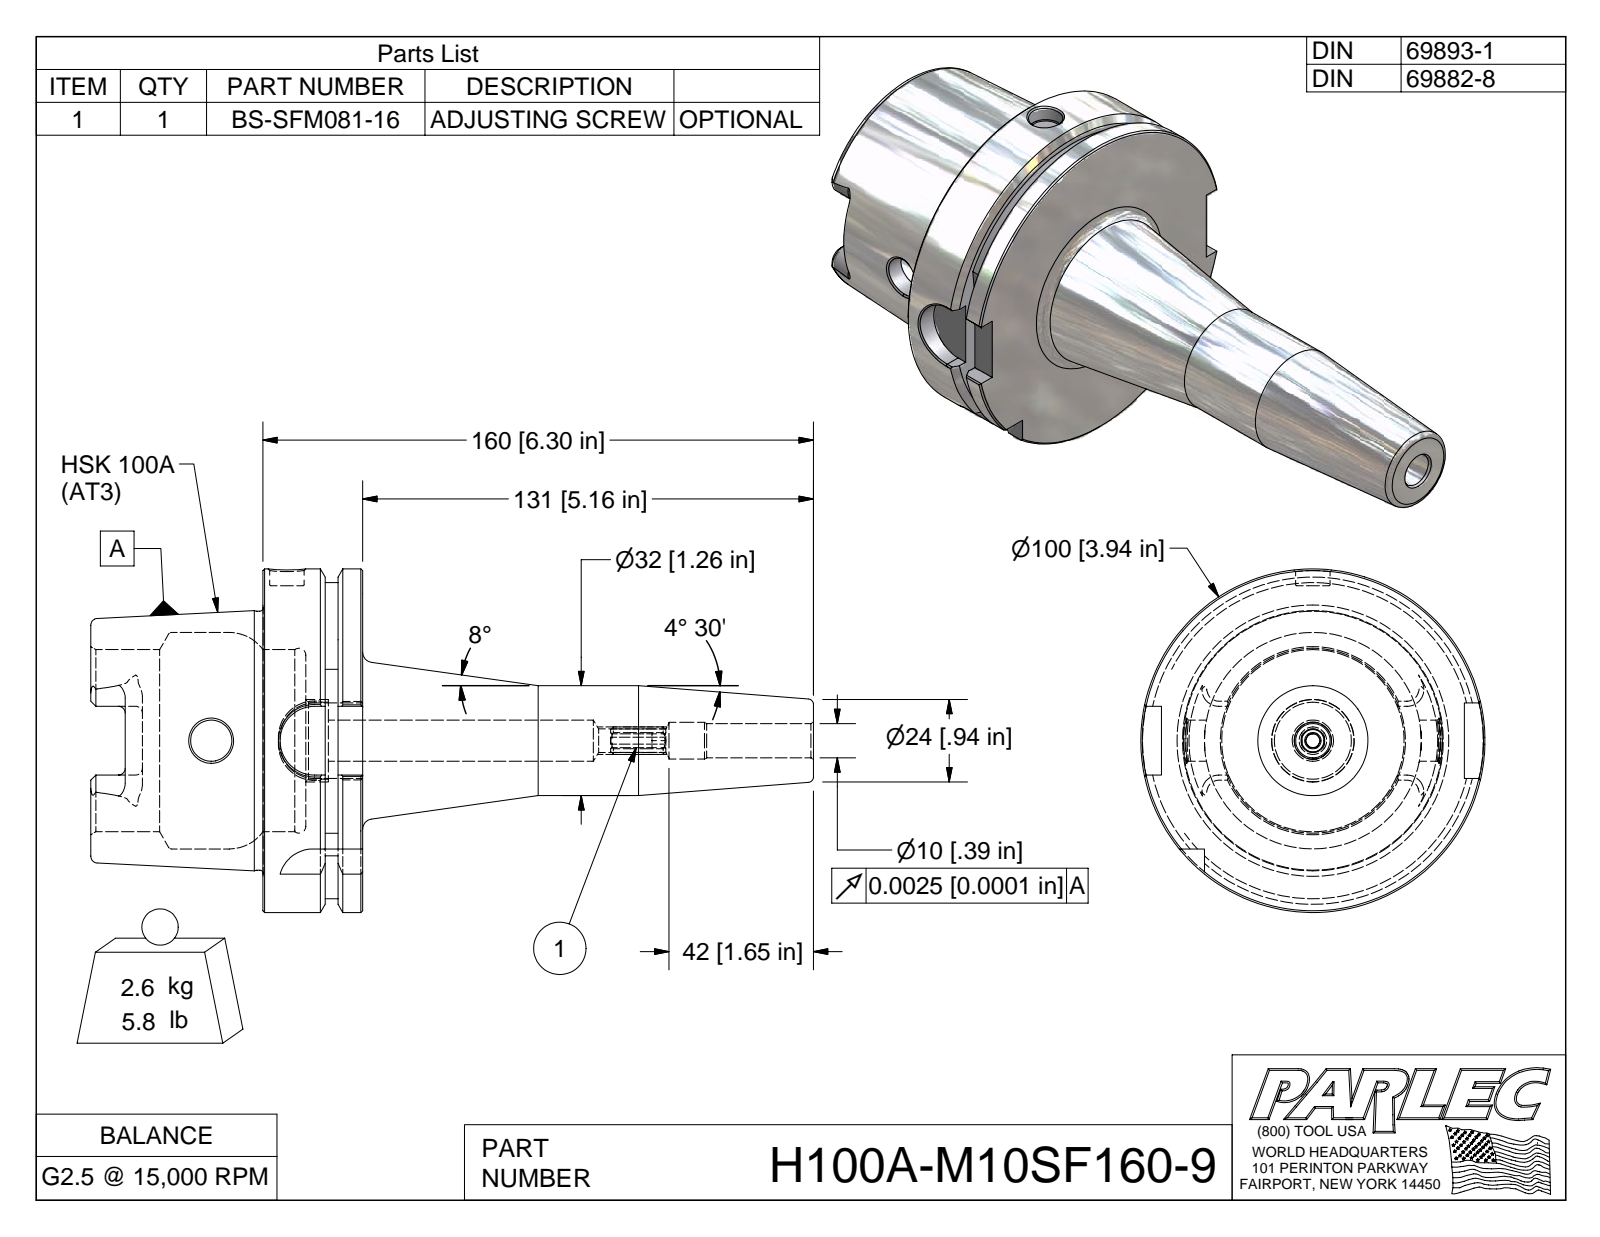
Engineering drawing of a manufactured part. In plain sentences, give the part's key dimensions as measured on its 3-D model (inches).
The part is named "H100A-M10SF160-9; H100A-M10SF160-9-1; BS-SFM081-16". Its 3-D file was written by "Autodesk Inventor 2009 (AUTOMOTIVE_DESIGN)". It is 2 solids with 148 faces: 48 planar, 29 cylindrical and 71 other. Overall it measures 8.269 by 3.937 by 3.937 inches. Its volume is 22.12 cubic inches and its surface area 103.5 square inches. Round holes: 1 of diameter 0.393, 1 of diameter 0.394, 1 of diameter 0.423, 1 of diameter 0.472, 1 of diameter 0.881, 1 of diameter 2.087, 1 of diameter 2.48. Round bosses or shafts: 1 of diameter 3.937, 1 of diameter 2.967, 1 of diameter 1.26. Partial cylindrical surfaces (rounded edges, fillets, slot ends): 4 of radius 0.394, 3 of radius 0.079, 2 of radius 0.192, 1 of radius 0.157, 1 of radius 1.811. The main face-to-face distances are 1.142, 0.492, 0.65, 1.969, 2.461, 3.11, 2.682, 0.713, 0.221, 0.428.
